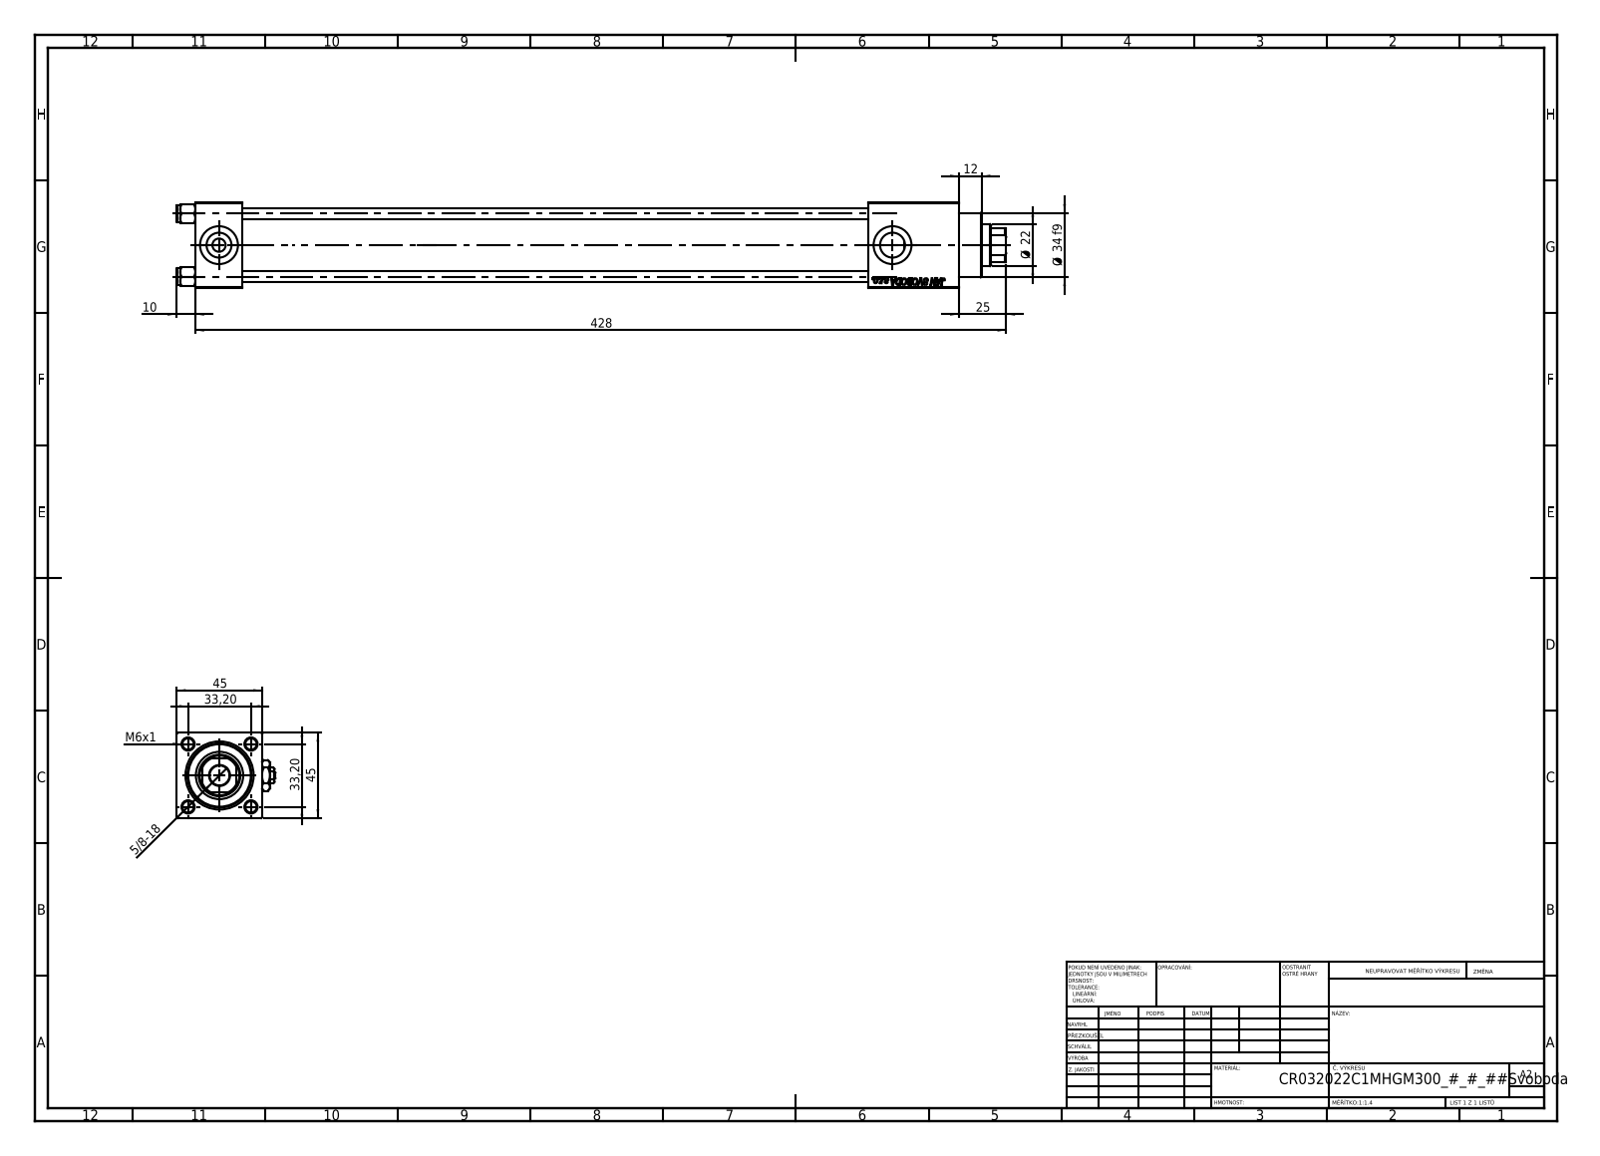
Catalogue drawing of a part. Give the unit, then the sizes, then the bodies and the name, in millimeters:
Units: millimetres
Overall size (bounding box): 438 × 52 × 45
Round holes (diameter × count): ⌀6 ×4, ⌀7 ×2, ⌀13.16 ×2, ⌀20 ×2, ⌀10.5 ×1, ⌀22 ×1, ⌀24 ×1, ⌀25 ×1, ⌀32 ×1, ⌀33 ×1
Round bosses / shafts (diameter × count): ⌀9 ×4, ⌀38 ×1, ⌀34 ×1
Partial cylindrical surfaces — rounded edges, fillets, slot ends (radius × count): R10.5 ×1
Main face-to-face distances: 45, 25, 403, 355, 330, 378, 48, 374.3, 349.3, 19.3
Hole centre spacings: 23.48, 33.2, 46.95, 355.5
Volume: 439 622 mm³ · Surface area: 174 103 mm²
Bodies: 12 solids, 1195 faces (549 planar, 90 cylindrical, 556 other)
Part name (STEP PRODUCT): V215CR_C_Body; V215CR_C_TYCINKA; V215_VC_A; V215CR_VCP_C (+2 more)
STEP written by: SolidWorks 2019 (CONFIG_CONTROL_DESIGN)
